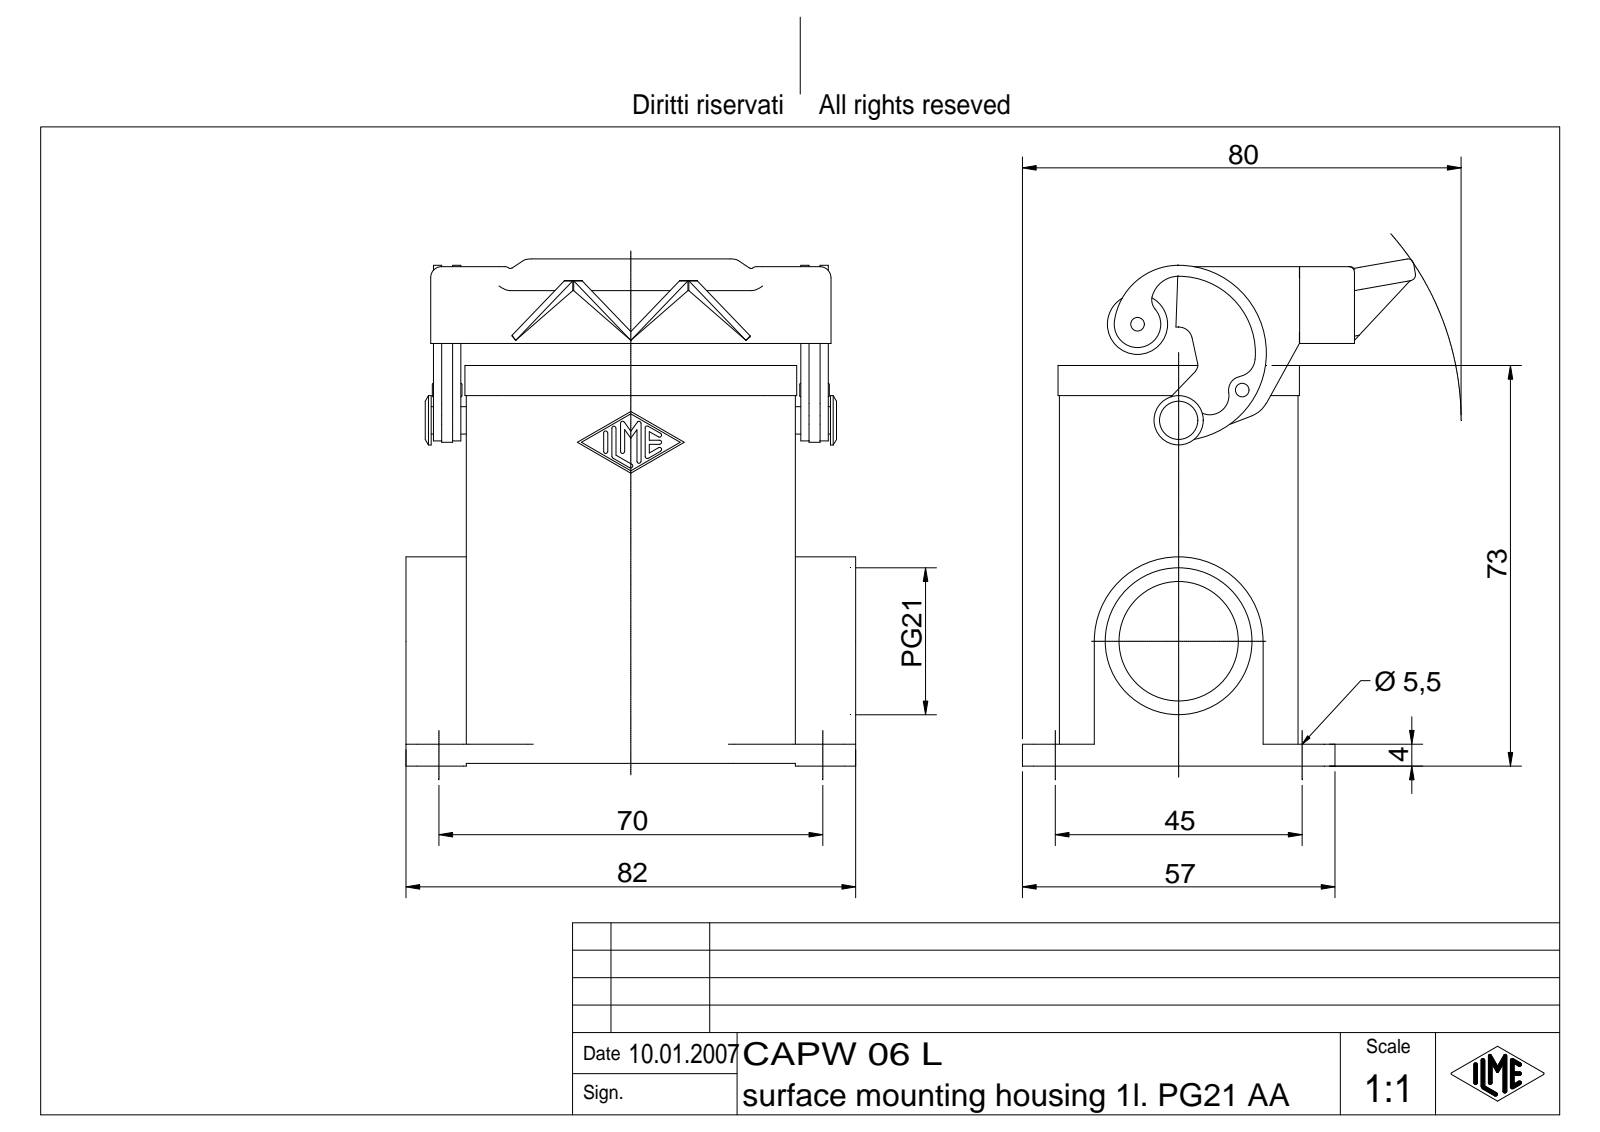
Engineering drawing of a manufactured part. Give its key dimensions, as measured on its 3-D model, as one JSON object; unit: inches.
{"part_name": "CAPW 06 L", "step_written_by": "Autodesk Inventor 7 (AUTOMOTIVE_DESIGN)", "units": "inches", "bodies": {"solids": 1, "faces": 492, "planar": 157, "cylindrical": 139, "other": 196}, "overall_size": [3.639, 3.228, 2.823], "volume_in3": 5.685, "surface_area_in2": 73.99, "round_holes": [[0.217, 2], [0.098, 1], [0.857, 1], [1.054, 1]], "round_bosses_or_shafts": [[0.433, 1], [0.354, 1], [0.197, 1], [0.118, 1], [0.079, 1]], "partial_cylinders_radius": [[0.079, 24], [0.015, 14], [0.236, 8], [0.039, 7], [0.118, 4], [0.059, 3], [0.098, 3], [0.138, 2]], "face_to_face_distances": [0.118, 1.594, 1.713, 0.157, 1.476, 0.138, 0.128, 0.03, 2.362, 2.717], "hole_center_spacings": [1.858, 3.276]}
